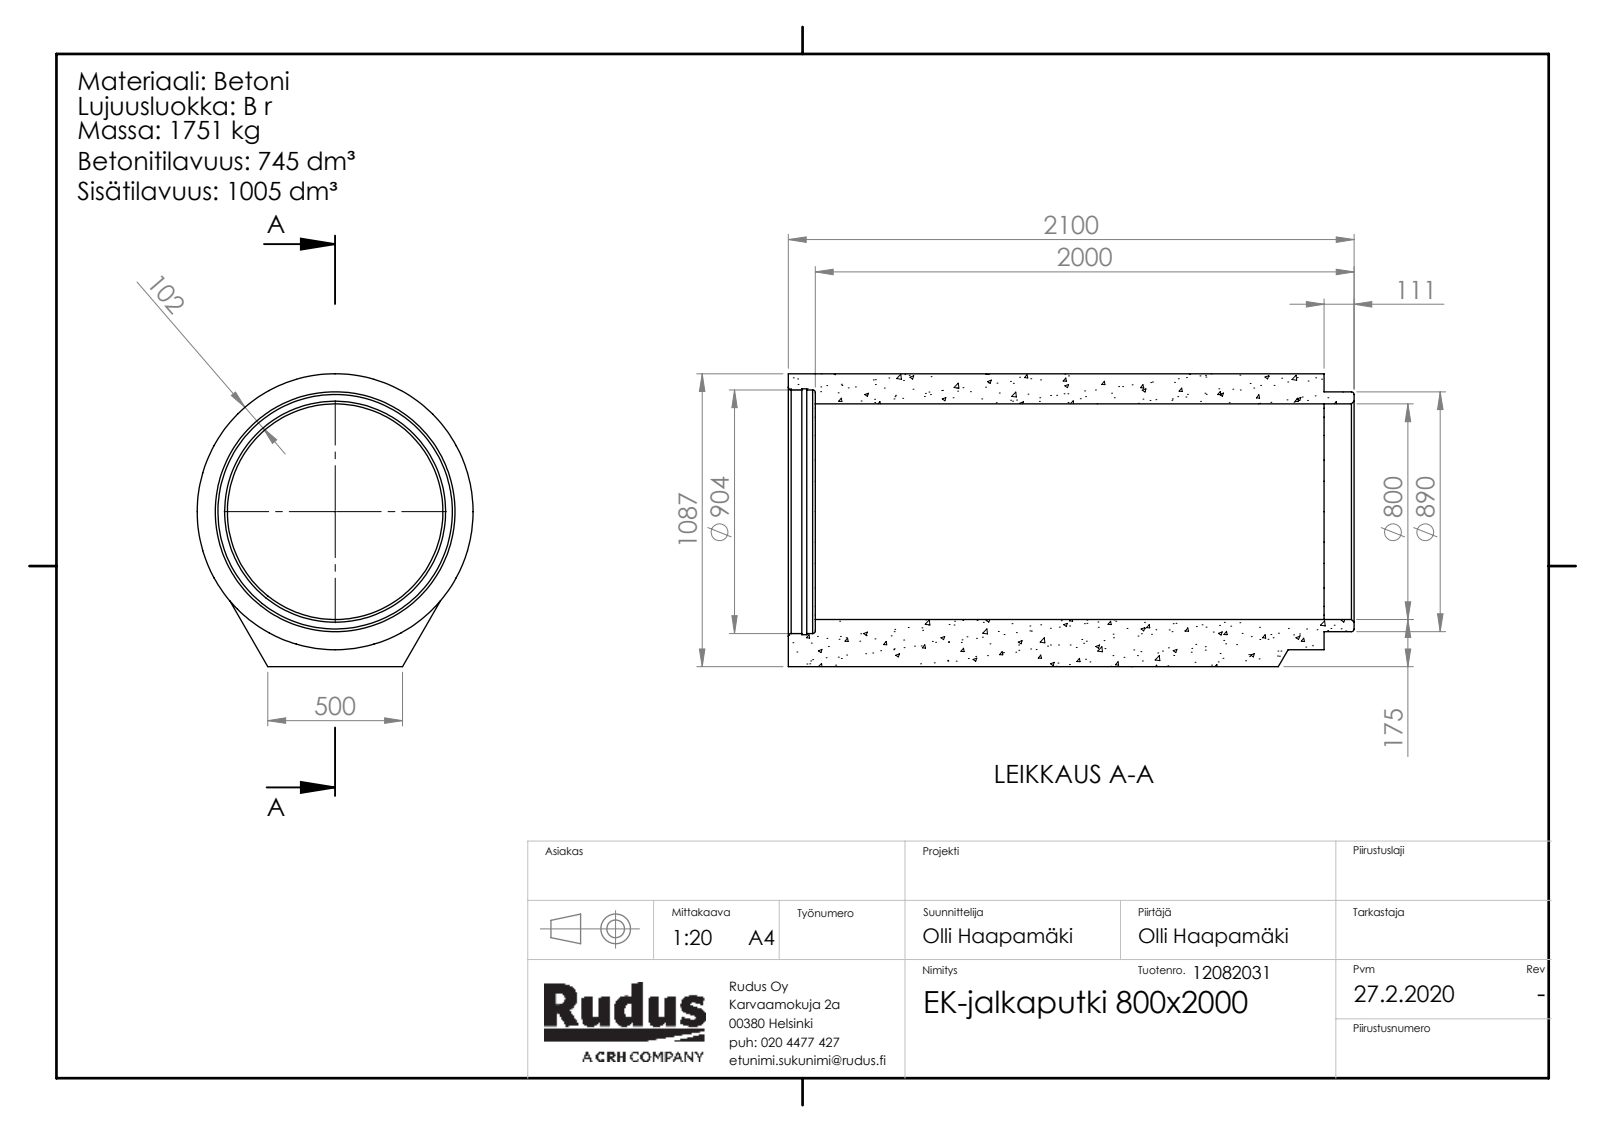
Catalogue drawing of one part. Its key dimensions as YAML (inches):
part_name: "Rudus 12082031 EK-jalkaputki 800x2000; EK-osa-putkirunko_Jalkaputki"
step_written_by: "SolidWorks 2019 (CONFIG_CONTROL_DESIGN)"
units: inches
bodies: {solids: 1, faces: 113, planar: 31, cylindrical: 14, other: 68}
overall_size: [82.677, 42.795, 40.315]
volume: 45380
surface_area: 21450
round_holes:
  - {diameter: 31.496, count: 1}
  - {diameter: 35.591, count: 1}
  - {diameter: 35.906, count: 1}
round_bosses_or_shafts:
  - {diameter: 35.039, count: 1}
partial_cylinders:
  - {radius: 20.157, count: 1}
face_to_face_distances: [78.307, 3.937, 74.37, 82.677, 78.74, 4.37, 1.969, 2.677, 1.26, 75.63]
